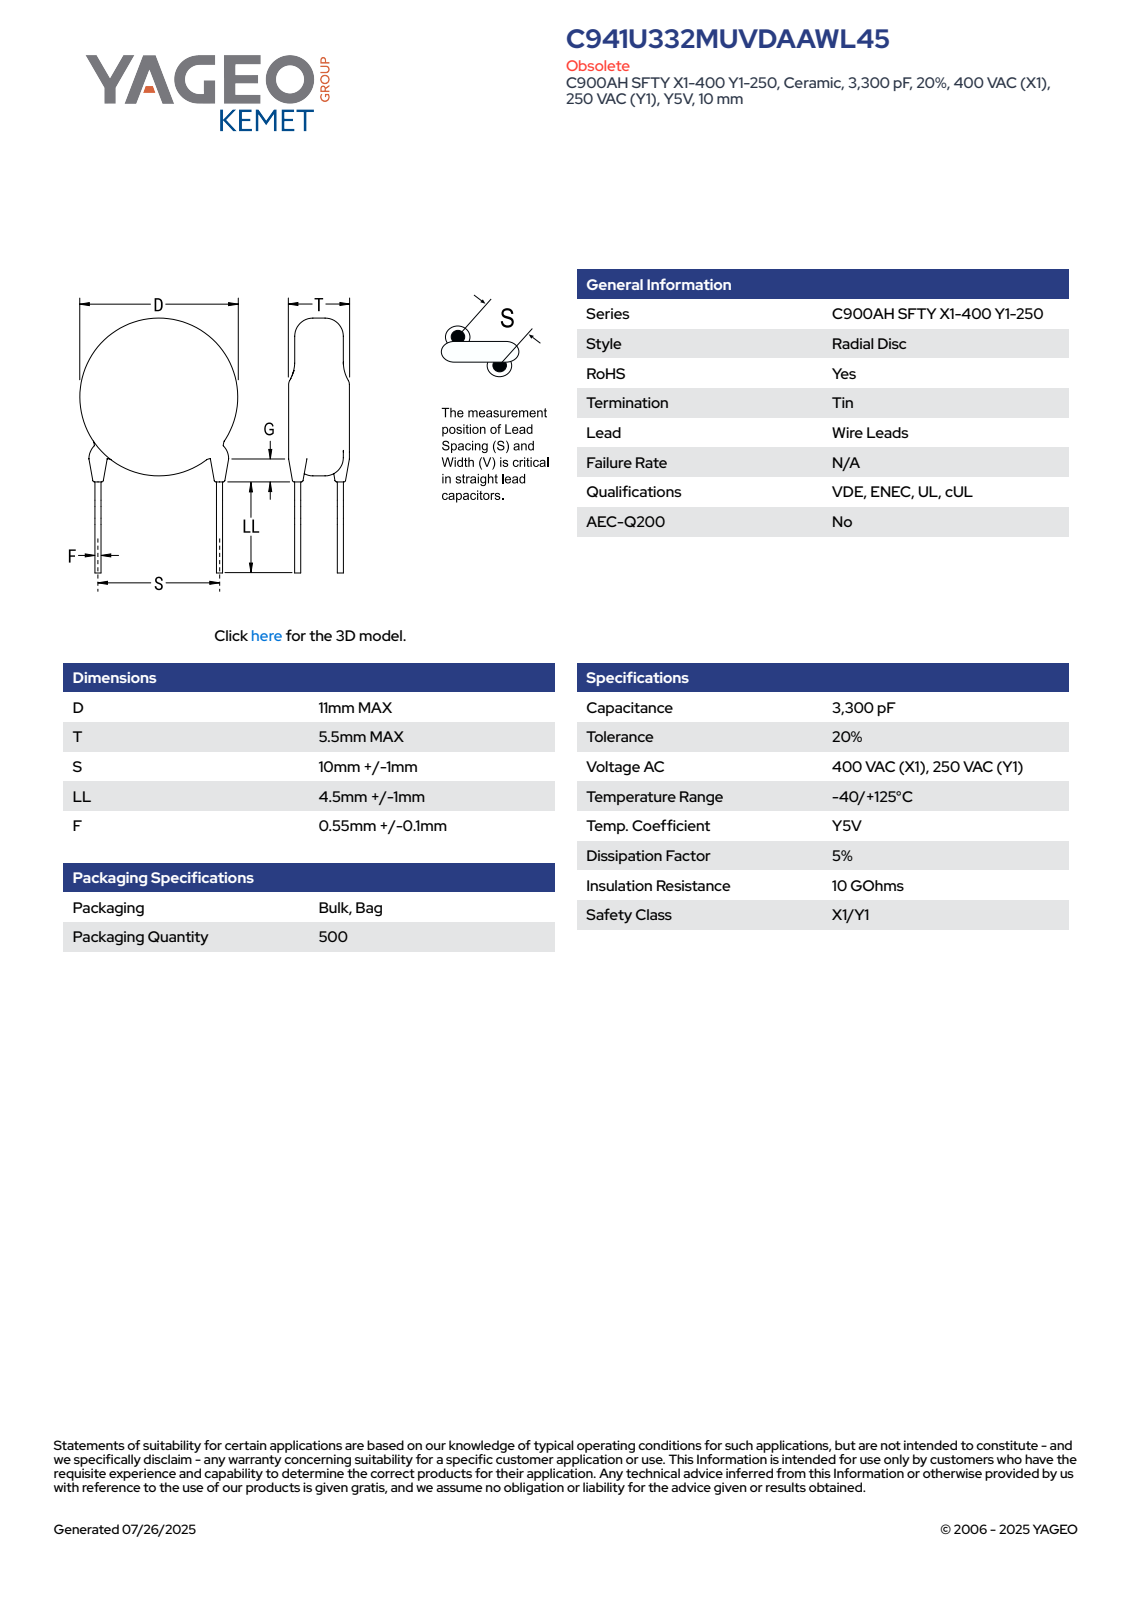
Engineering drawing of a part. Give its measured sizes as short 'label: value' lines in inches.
name: CCD_STC900_D11T5.5S10LL5.5F0.65G3
written by: SolidWorks 2014 (AUTOMOTIVE_DESIGN)
unit: in
bodies: 4 solids, 83 faces (61 planar, 6 cylindrical, 16 other)
size: 0.663 × 0.433 × 0.217
volume: 0.031 in³; area: 0.611 in²
bosses: 2× ⌀0.026, 1× ⌀0.433
face distances: 0.217, 0.05, 0.471, 0.421, 0.014, 0.041, 0.204, 0.031, 0.148, 0.154
